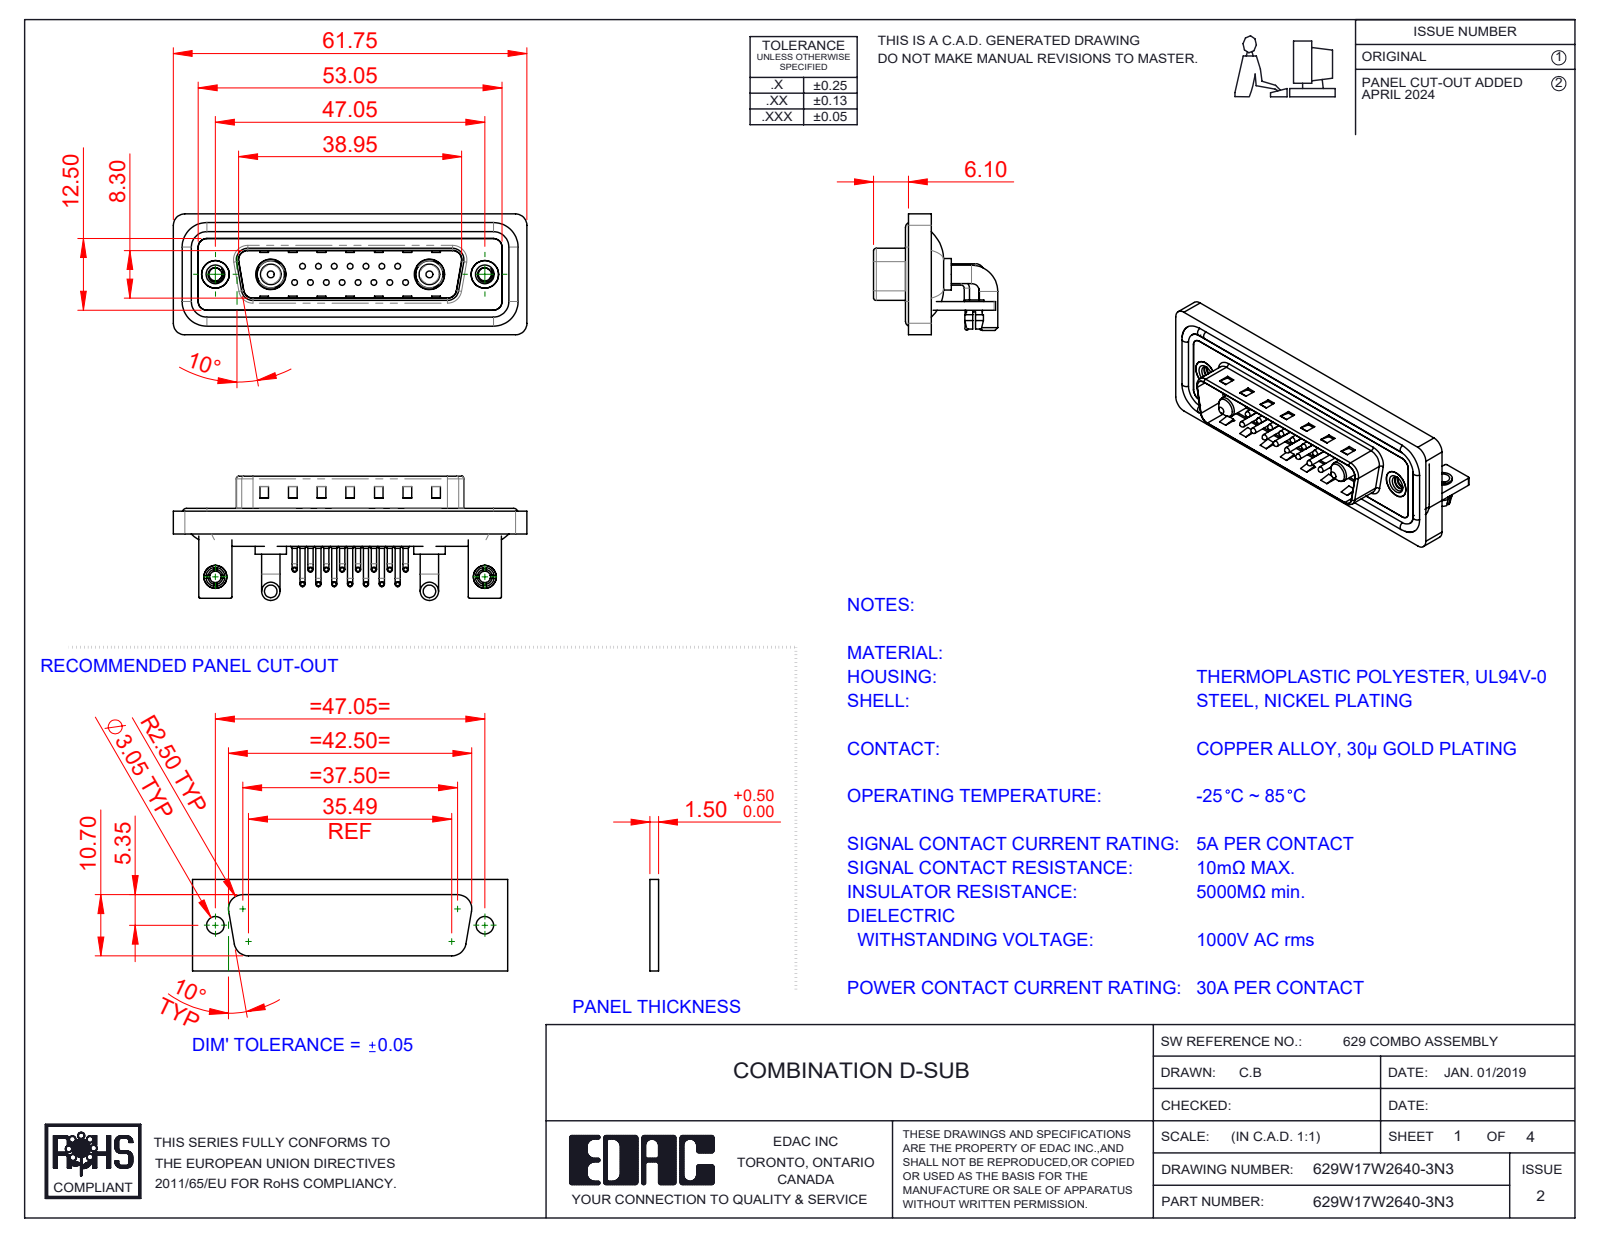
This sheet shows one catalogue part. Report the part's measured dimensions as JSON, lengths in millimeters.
{"part_name": "629Combo Shell Rear_25 Contacts; 629Combo Waterproof Housing_25 Contacts; 629Combo Stabilizer Bracket; 629Combo Housing_17W2 (+7 more)", "step_written_by": "SolidWorks 2023 (CONFIG_CONTROL_DESIGN)", "units": "millimeters", "bodies": {"solids": 30, "faces": 2351, "planar": 1257, "cylindrical": 820, "other": 274}, "overall_size": [61.75, 21.7, 21.1], "volume_mm3": 7882, "surface_area_mm2": 13435, "round_holes": [[2, 17], [0.75, 15], [1.6, 15], [2.26, 2], [2.5, 2], [3.2, 2], [4, 2], [4.8, 2], [4.85, 2], [5, 2], [5.3, 2]], "round_bosses_or_shafts": [[0.9, 30], [1.5, 15], [1, 15], [0.65, 15], [3.2, 4], [1.6, 4], [5.5, 2], [5.2, 2]], "partial_cylinders_radius": [[2, 19], [1.5, 18], [0.25, 16], [1.01, 15], [0.5, 9], [1.6, 8], [0.6, 4], [0.65, 4]], "face_to_face_distances": [0.4, 0.8, 1.5, 2.1, 2.9, 1.1, 4.1, 1.6, 4.5, 3.7], "hole_center_spacings": [3.16, 2.77, 5.54, 8.31, 5.04, 7.49, 11.08, 5.03]}
